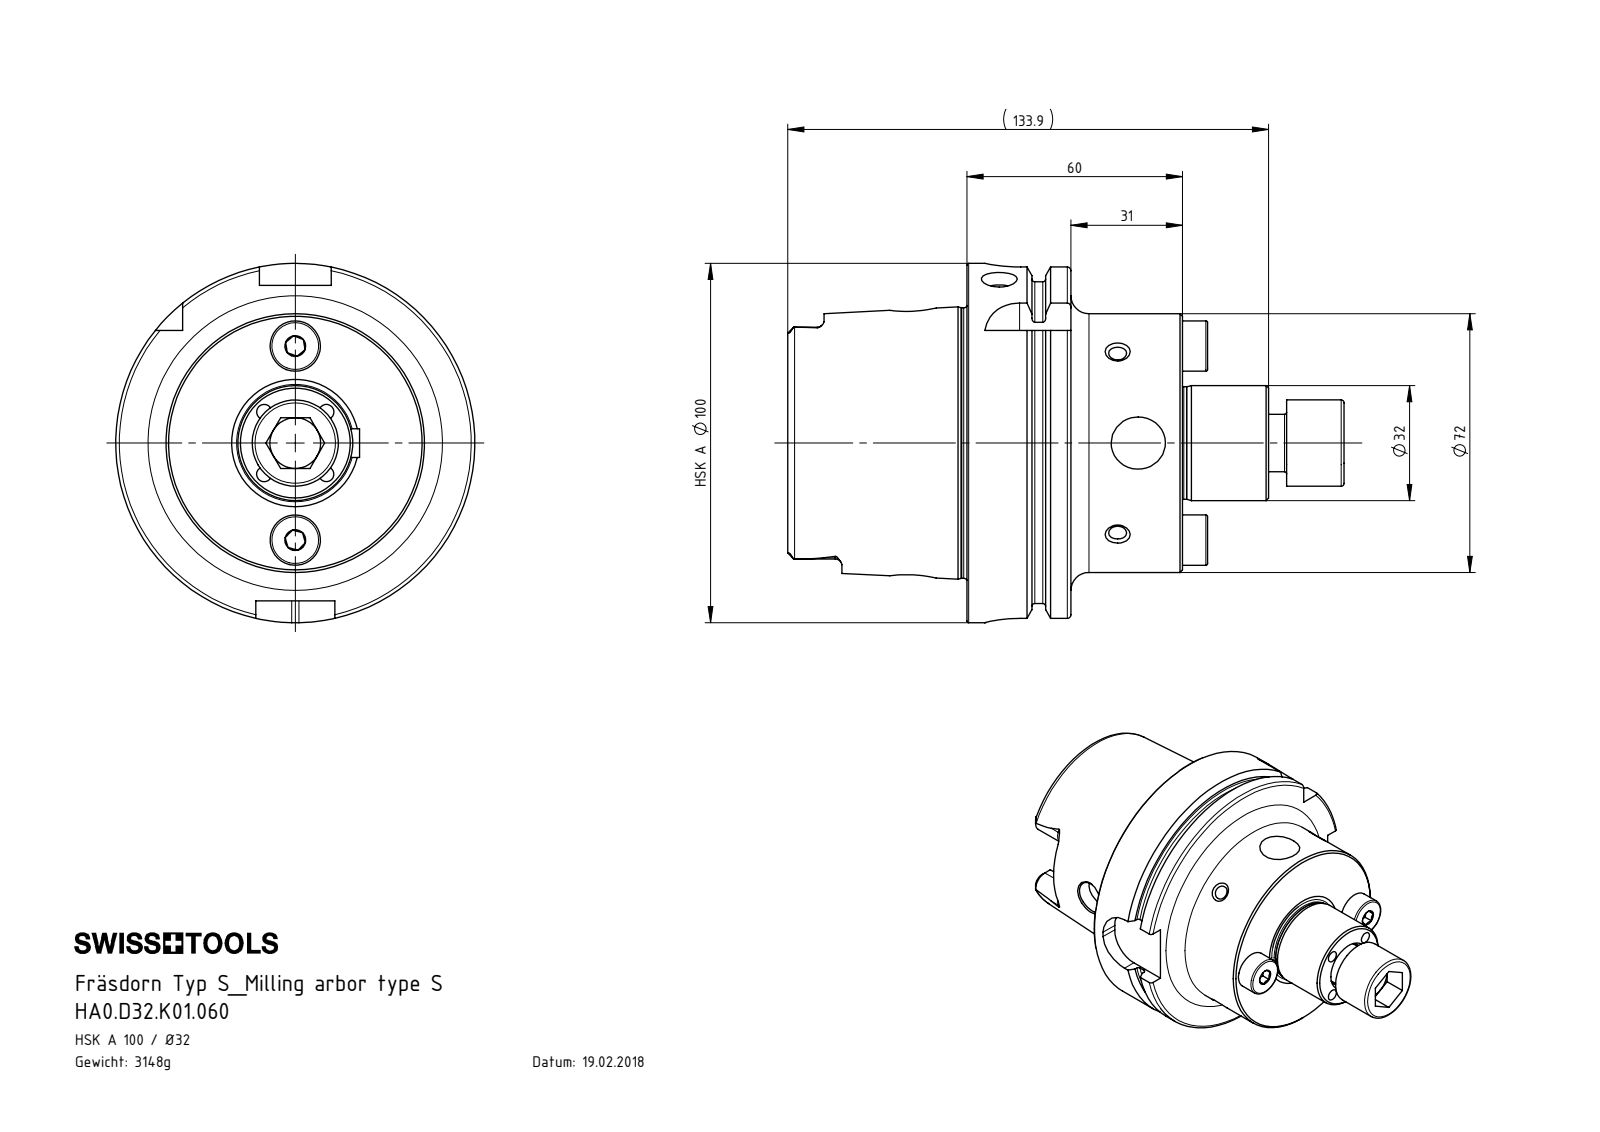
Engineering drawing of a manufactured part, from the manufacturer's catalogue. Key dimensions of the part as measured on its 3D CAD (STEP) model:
Part name (STEP PRODUCT): DIN 6885 - 8x7x16; HA0.D32.K01.060; D32-ER1.002.035_A; D32-ER2.001.022_B (+1 more)
STEP written by: SolidWorks 2017 (AUTOMOTIVE_DESIGN)
Units: millimetres
Bodies: 5 solids, 369 faces (89 planar, 119 cylindrical, 161 other)
Overall size (bounding box): 154.9 × 100 × 100
Volume: 401 013 mm³ · Surface area: 72 040 mm²
Round holes (diameter × count): ⌀4.2 ×6, ⌀5 ×6, ⌀12 ×4, ⌀10 ×3, ⌀14 ×1, ⌀17 ×1, ⌀22.5 ×1, ⌀26 ×1, ⌀53 ×1, ⌀63 ×1
Round bosses / shafts (diameter × count): ⌀14 ×2, ⌀6 ×2, ⌀4.6 ×2, ⌀100 ×1, ⌀91.95 ×1, ⌀75.26 ×1, ⌀72 ×1, ⌀32 ×1
Partial cylindrical surfaces — rounded edges, fillets, slot ends (radius × count): R1.9 ×6, R4 ×4, R4.88 ×4, R10 ×4
Main face-to-face distances: 60, 28.95, 31.05, 12.45, 16.5, 47.55, 49.9, 62.35, 78.85, 109.9
Hole centre spacings: 8.05, 12.25, 17.32, 20.28, 36.7, 24.49, 27, 54
